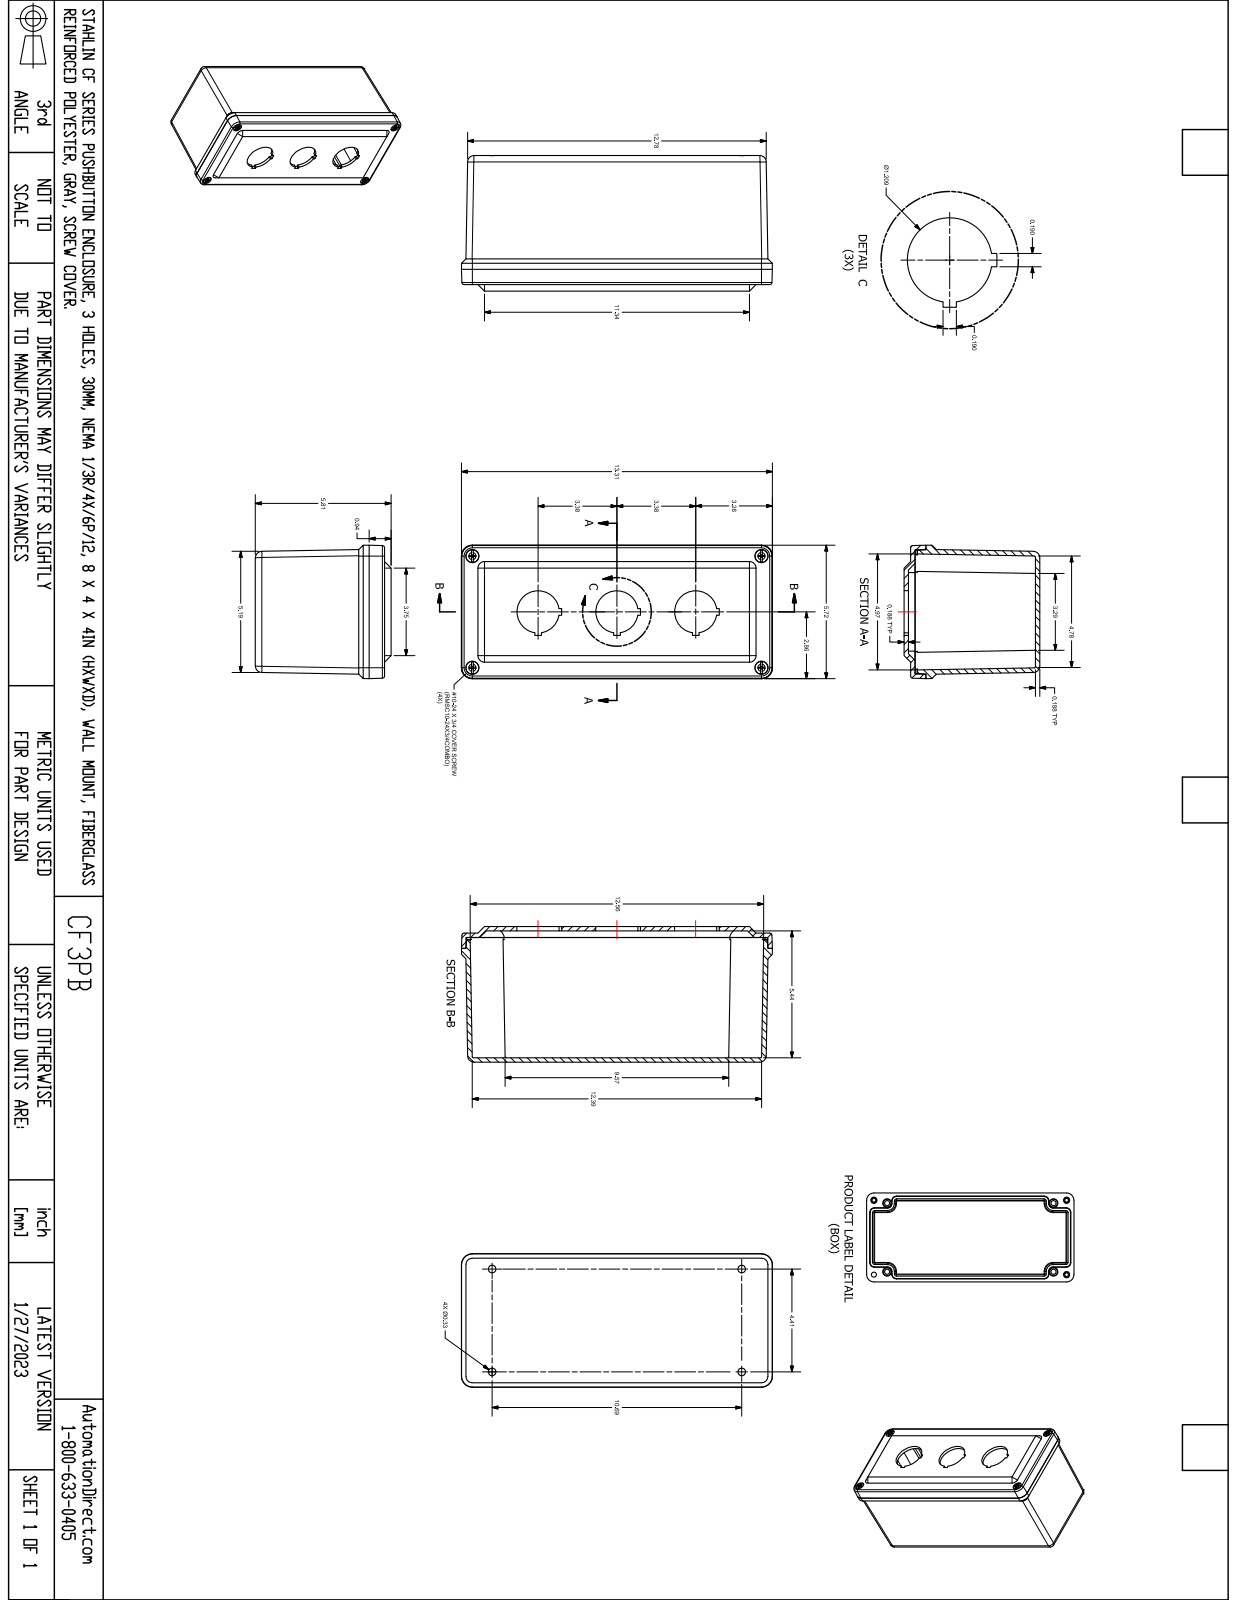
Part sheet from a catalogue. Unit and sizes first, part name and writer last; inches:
Units: inches
Overall size (bounding box): 8.875 × 3.875 × 3.812
Round holes (diameter × count): ⌀0.219 ×8, ⌀0.159 ×4, ⌀0.19 ×4, ⌀0.375 ×4, ⌀1.21 ×3
Round bosses / shafts (diameter × count): ⌀0.371 ×4, ⌀0.27 ×4, ⌀0.177 ×4
Partial cylindrical surfaces — rounded edges, fillets, slot ends (radius × count): R0.031 ×20, R0.012 ×16, R0.063 ×4, R0.176 ×4, R0.188 ×4, R0.22 ×4, R0.313 ×4, R0.325 ×4
Main face-to-face distances: 0.131, 0.125, 3.563, 0.5, 0.313, 0.125, 3.875, 3.75, 3.75, 3.625
Hole centre spacings: 3.114, 8.275, 3.187, 0.576, 1.97, 2.461, 3.854, 4.422
Volume: 24.3 in³ · Surface area: 331.7 in²
Bodies: 11 solids, 403 faces (201 planar, 106 cylindrical, 96 other)
Part name (STEP PRODUCT): CO3PB
STEP written by: SolidWorks 2018 (AUTOMOTIVE_DESIGN)
